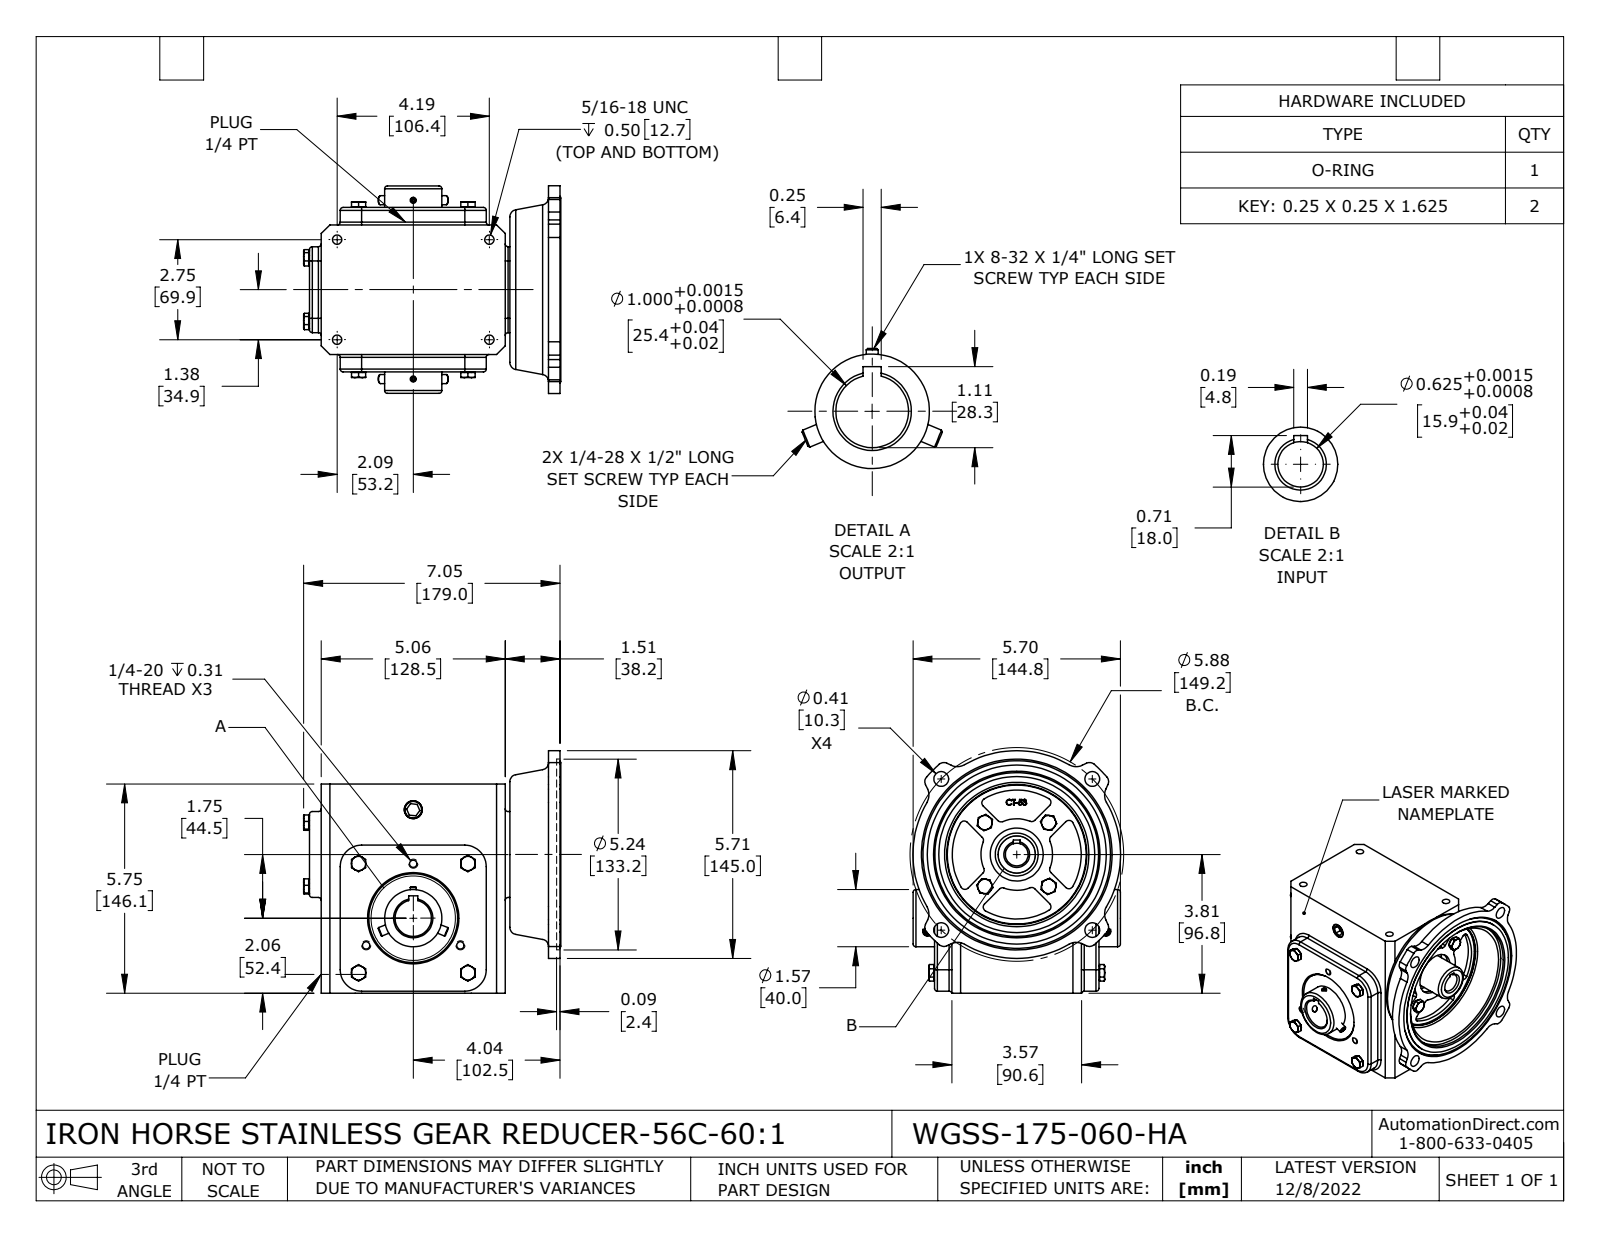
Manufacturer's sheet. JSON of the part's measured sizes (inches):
{"part_name": "WGSS-175-060-HA", "step_written_by": "SolidWorks 2021 (CONFIG_CONTROL_DESIGN)", "units": "inches", "bodies": {"solids": 7, "faces": 891, "planar": 390, "cylindrical": 231, "other": 270}, "overall_size": [7.071, 6.691, 5.709], "volume_in3": 127, "surface_area_in2": 281, "round_holes": [[0.213, 4], [0.257, 4], [0.406, 4], [0.201, 3], [0.136, 2], [0.625, 1], [0.866, 1], [1, 1], [1.102, 1], [1.457, 1], [1.575, 1], [3.819, 1]], "round_bosses_or_shafts": [[0.394, 8], [0.25, 4], [0.164, 2], [4.921, 1], [2.441, 1], [1.575, 1], [1.181, 1]], "partial_cylinders_radius": [[0.079, 28], [0.118, 16], [0.394, 12], [0.197, 8], [0.591, 4], [0.984, 1], [1.772, 1], [2.854, 1]], "face_to_face_distances": [0.48, 4.04, 5.75, 5.06, 0.157, 3.56, 4.52, 0.315, 6.565, 1.506], "hole_center_spacings": [2.357, 2.937, 4.154, 1.496, 2.591, 4.913, 2.75, 4.188]}
